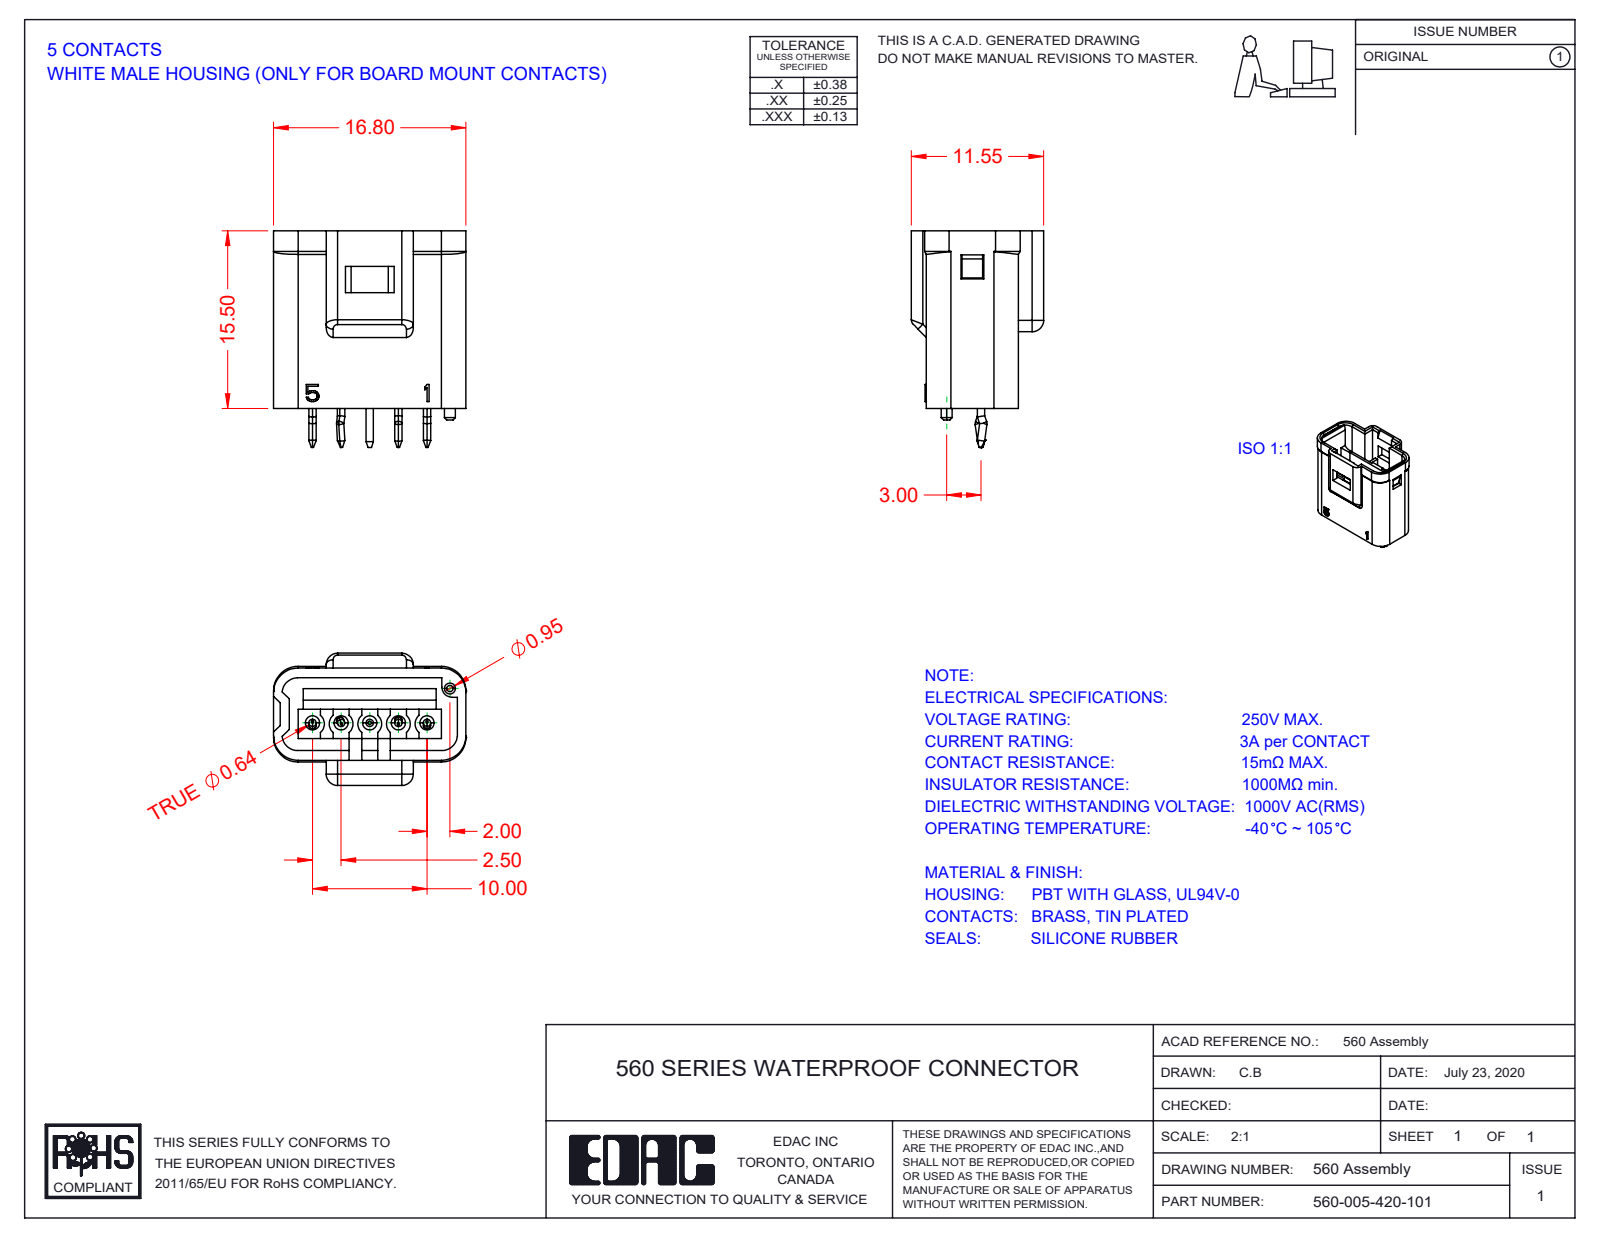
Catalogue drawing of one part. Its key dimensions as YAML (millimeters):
part_name: "CONTACT_PCB-HEADER; CONTACT_PCB-HEADER-1; PCB-HEADER-CONTACT-5P; CONTACT_PCB-HEADER-3 (+5 more)"
step_written_by: "SolidWorks 2020 (CONFIG_CONTROL_DESIGN)"
units: millimeters
bodies: {solids: 8, faces: 772, planar: 448, cylindrical: 184, other: 140}
overall_size: [18.9, 16.8, 11.55]
volume: 1028
surface_area: 2869
round_holes:
  - {diameter: 0.64, count: 5}
  - {diameter: 1.4, count: 5}
  - {diameter: 1.1, count: 1}
round_bosses_or_shafts:
  - {diameter: 0.64, count: 8}
  - {diameter: 0.95, count: 1}
partial_cylinders:
  - {radius: 1, count: 25}
  - {radius: 0.25, count: 16}
  - {radius: 0.35, count: 12}
  - {radius: 1.65, count: 8}
  - {radius: 2.15, count: 8}
  - {radius: 0.3, count: 4}
  - {radius: 0.5, count: 4}
  - {radius: 1.1, count: 4}
face_to_face_distances: [0.6, 7.45, 3.6, 8.05, 1.1, 7.4, 6.8, 1.9, 6.85, 2.5]
hole_center_spacings: [2.5, 5, 3.14, 5.35, 7.5, 1.9, 10]
